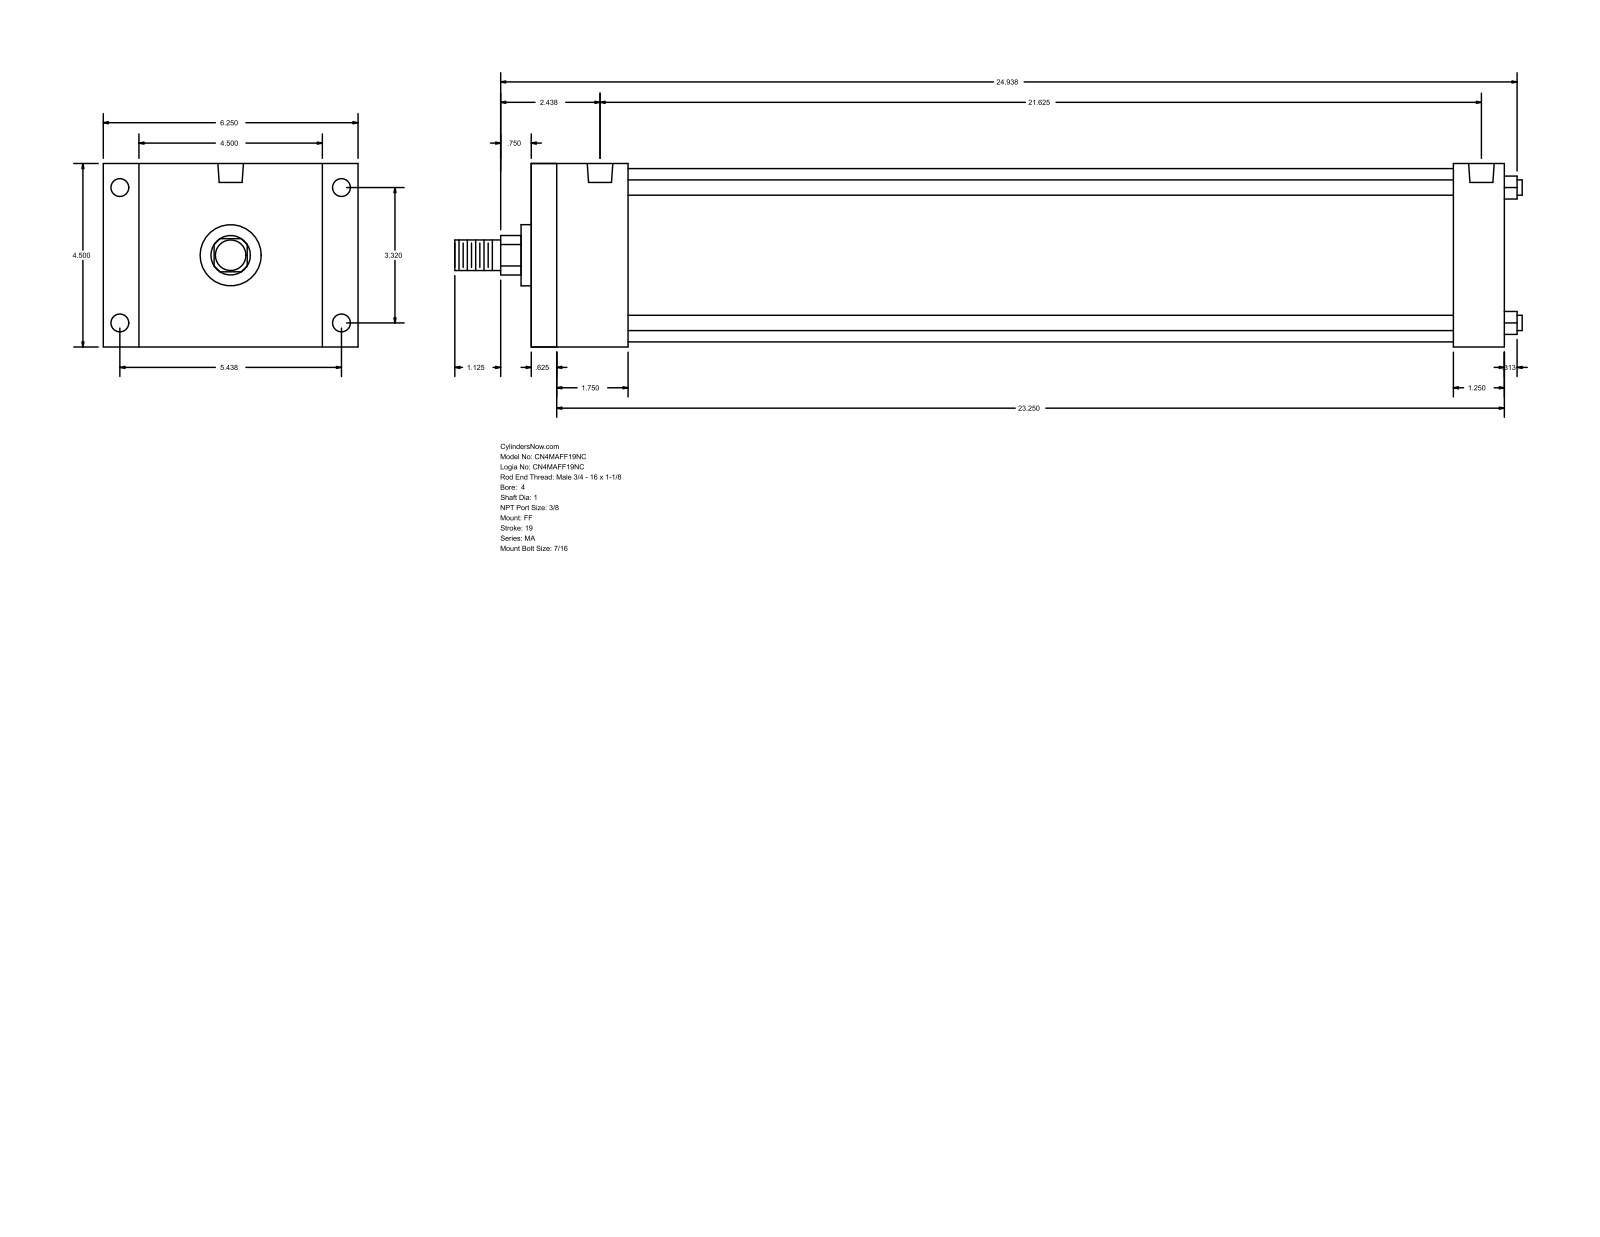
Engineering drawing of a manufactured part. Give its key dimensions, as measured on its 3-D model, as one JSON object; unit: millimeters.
{"part_name": "MA_FF__0400_1", "step_written_by": "GSSL Pune (CONFIG_CONTROL_DESIGN)", "units": "millimeters", "bodies": {"solids": 0, "faces": 92, "planar": 64, "cylindrical": 28, "other": 0}, "overall_size": [665.16, 158.75, 114.3], "round_holes": [[11.11, 8], [15.93, 2]], "round_bosses_or_shafts": [[9.53, 4], [107.95, 1], [38.1, 1], [25.4, 1], [19.05, 1]], "partial_cylinders_radius": [[12.29, 1]], "face_to_face_distances": [114.3, 606.43, 15.87, 590.56, 22.23, 136.53, 574.68, 558.81, 31.75, 60.33], "hole_center_spacings": [84.32, 138.12, 161.82, 539.75, 4.76, 4.77, 544.51, 544.52]}
